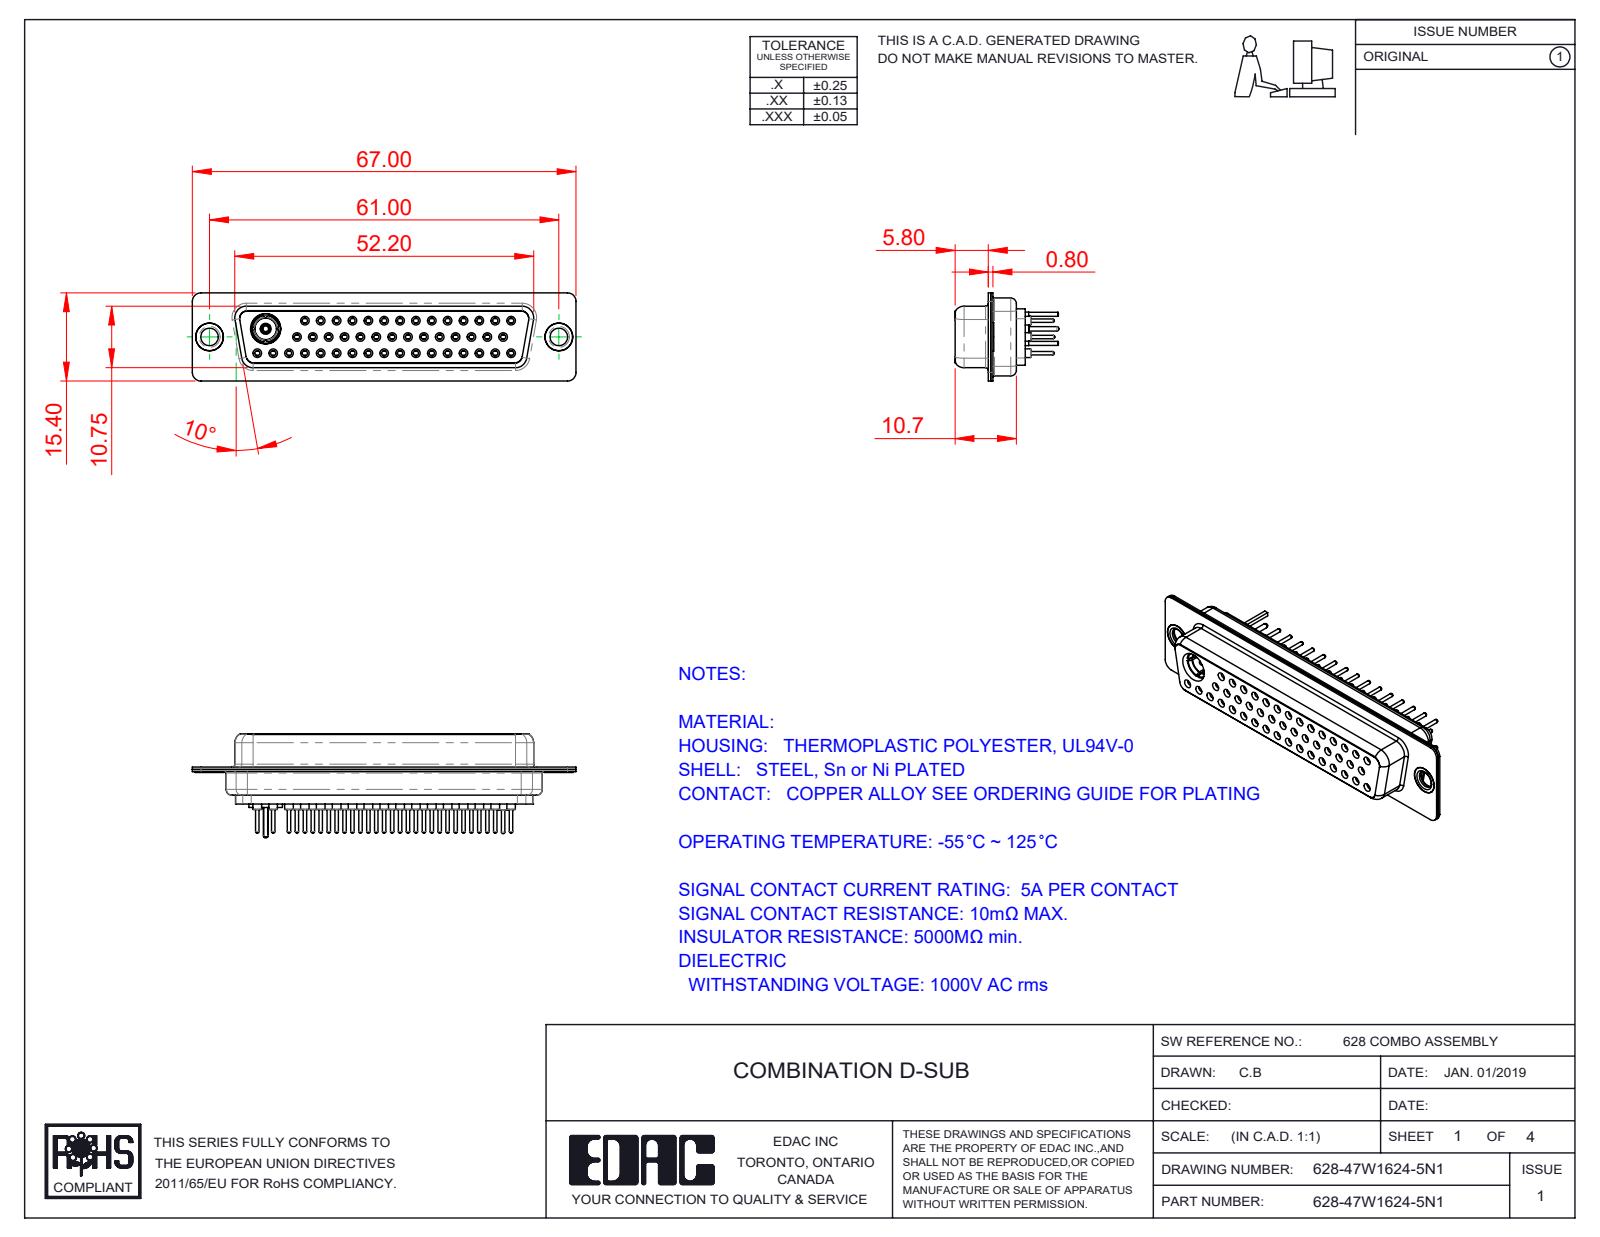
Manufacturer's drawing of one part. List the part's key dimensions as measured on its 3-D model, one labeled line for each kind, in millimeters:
Part name (STEP PRODUCT): 628-47W1624-5N1; Co-Ax Plug_Straight PC Tail; Pin_Str; 628Combo Contact Row 2_24 (+8 more)
STEP written by: SolidWorks 2016 (CONFIG_CONTROL_DESIGN)
Units: millimetres
Bodies: 55 solids, 2897 faces (811 planar, 1032 cylindrical, 1054 other)
Overall size (bounding box): 67 × 18.15 × 15.4
Volume: 6 967 mm³ · Surface area: 14 734 mm²
Round holes (diameter × count): ⌀1.1 ×47, ⌀1.5 ×46, ⌀0.9 ×45, ⌀2 ×45, ⌀1.6 ×31, ⌀1.7 ×14, ⌀4.85 ×3, ⌀3.05 ×2, ⌀4 ×2, ⌀4.05 ×2, ⌀2.83 ×1, ⌀3.3 ×1
Round bosses / shafts (diameter × count): ⌀2.2 ×46, ⌀0.6 ×46, ⌀1.6 ×15, ⌀5 ×3, ⌀4.95 ×2, ⌀4.8 ×2, ⌀3.55 ×2, ⌀5.85 ×1
Partial cylindrical surfaces — rounded edges, fillets, slot ends (radius × count): R1.5 ×16, R1.35 ×12, R2 ×12, R1.6 ×8, R0.25 ×4, R0.5 ×4, R0.6 ×4, R0.65 ×4
Main face-to-face distances: 0.4, 6.45, 6.05, 11.33, 1.87, 12.25, 6.2, 5.8, 10.35, 10.93
Hole centre spacings: 3.16, 2.77, 5.54, 8.31, 11.08, 13.85, 16.62, 19.39
